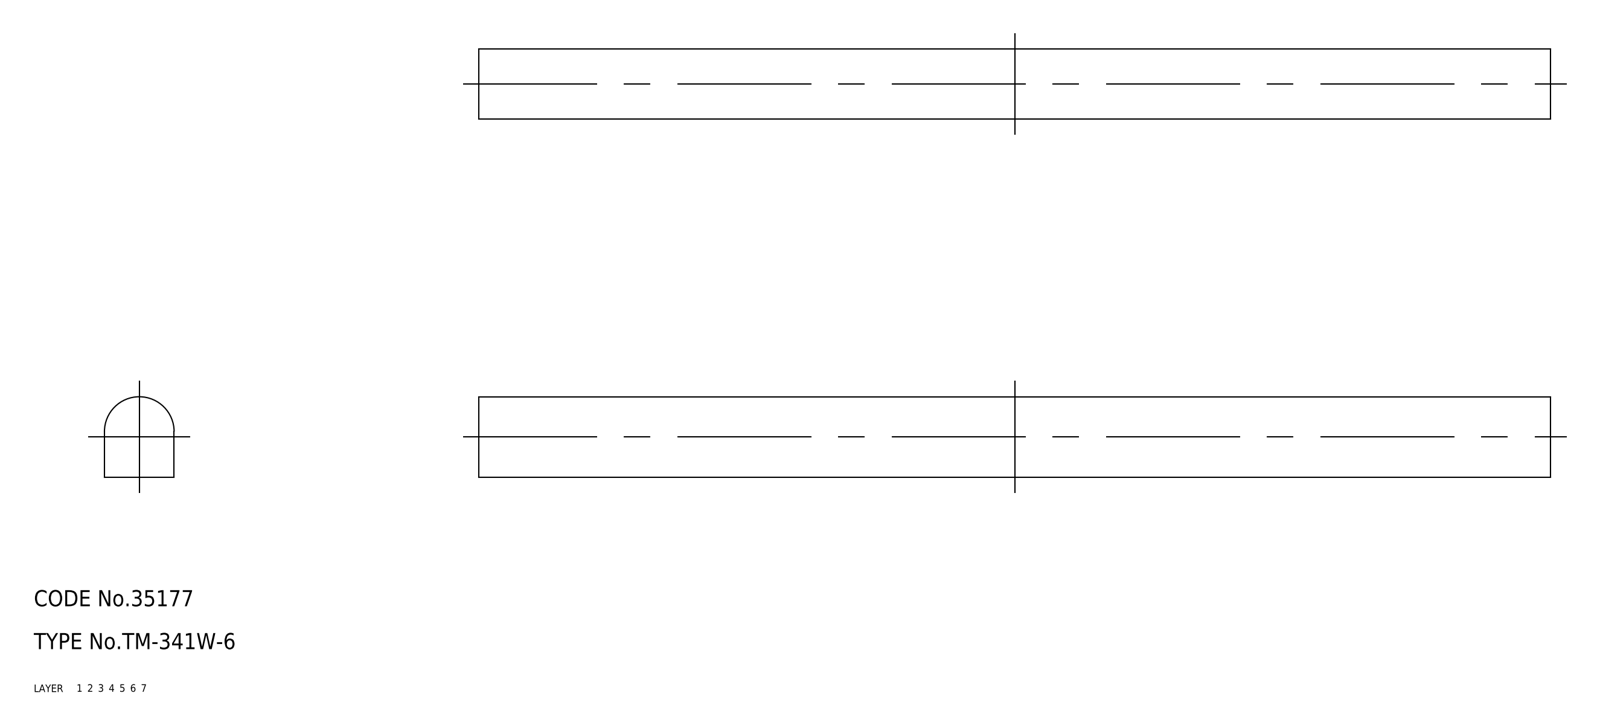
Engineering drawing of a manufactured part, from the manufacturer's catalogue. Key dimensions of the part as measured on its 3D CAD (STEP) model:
Part name (STEP PRODUCT): TM_341W_6; rubber foam
STEP written by: SolidWorks 2015 (AUTOMOTIVE_DESIGN)
Units: millimetres
Bodies: 1 solid, 6 faces (5 planar, 1 cylindrical, 0 other)
Overall size (bounding box): 200 × 15 × 13
Volume: 35 373 mm³ · Surface area: 10 438 mm²
Partial cylindrical surfaces — rounded edges, fillets, slot ends (radius × count): R6.5 ×1
Main face-to-face distances: 13, 200
